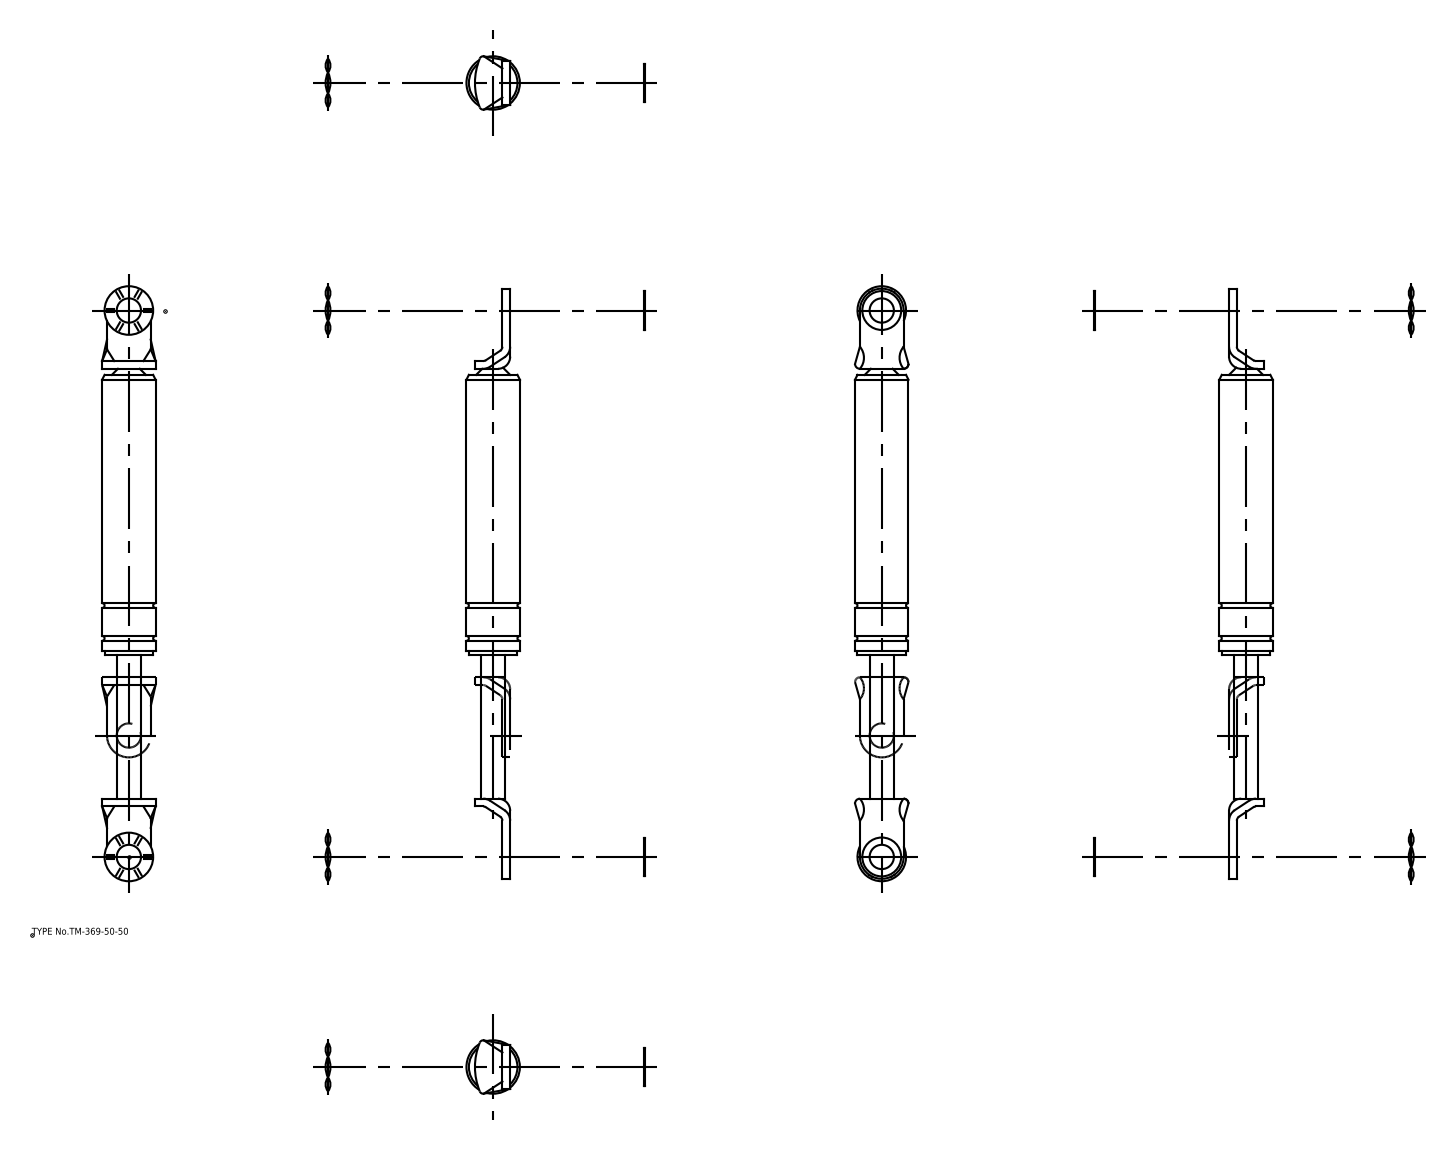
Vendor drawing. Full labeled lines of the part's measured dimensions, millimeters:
Part name (STEP PRODUCT): ウェーブワッシャー; ワッシャー; 本体; 本体_div
STEP written by: spGate 16.7.1 (AUTOMOTIVE_DESIGN)
Units: millimetres
Bodies: 6 solids, 95 faces (43 planar, 44 cylindrical, 8 other)
Overall size (bounding box): 245 × 22.5 × 22.5
Volume: 54 225 mm³ · Surface area: 16 292 mm²
Round holes (diameter × count): ⌀10 ×2
Round bosses / shafts (diameter × count): ⌀20 ×3, ⌀16 ×2, ⌀22.5 ×1, ⌀22 ×1, ⌀10 ×1
Partial cylindrical surfaces — rounded edges, fillets, slot ends (radius × count): R4.4 ×2, R5 ×2, R9 ×2, R26.32 ×1
Main face-to-face distances: 3.2, 2, 5.2, 5.7, 180.2, 3.7, 0.5, 121.2, 62.2, 183.4
Hole centre spacings: 225
